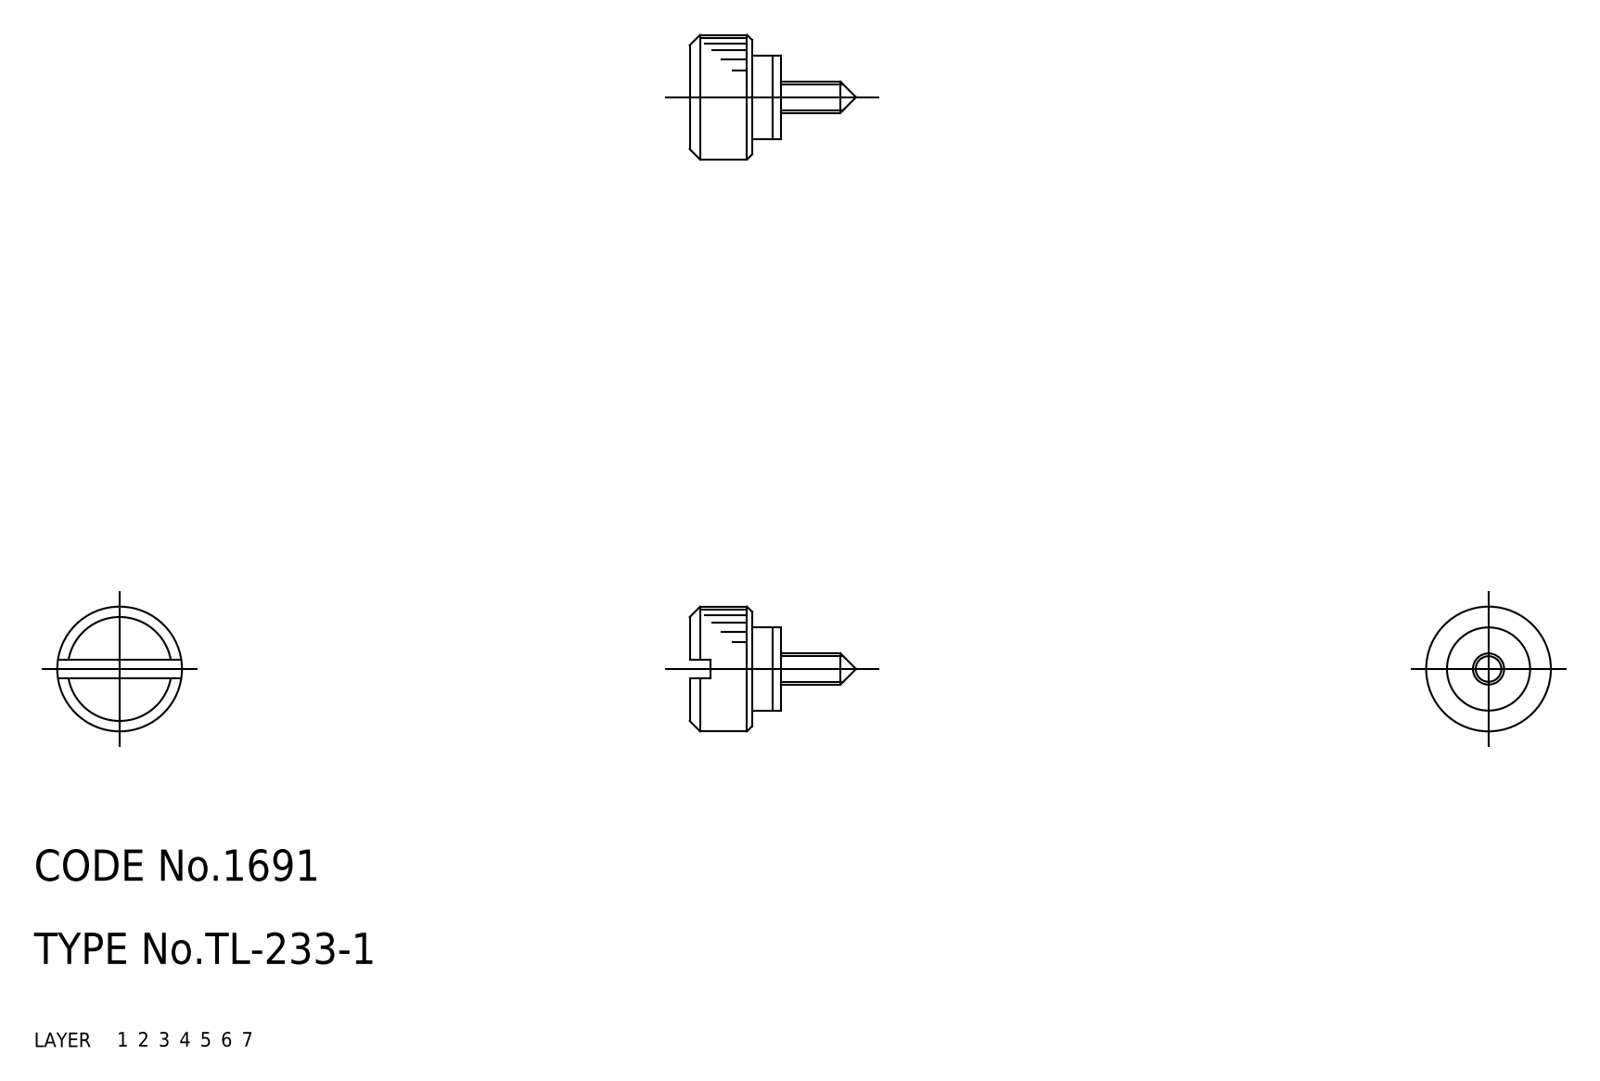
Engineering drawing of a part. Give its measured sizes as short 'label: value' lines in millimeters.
name: washer; knob; TL_233_1_28944_36
written by: CADfix (AUTOMOTIVE_DESIGN)
unit: mm
bodies: 2 solids, 37 faces (0 planar, 0 cylindrical, 37 other)
size: 16 × 12 × 12
volume: 798 mm³; area: 679 mm²
